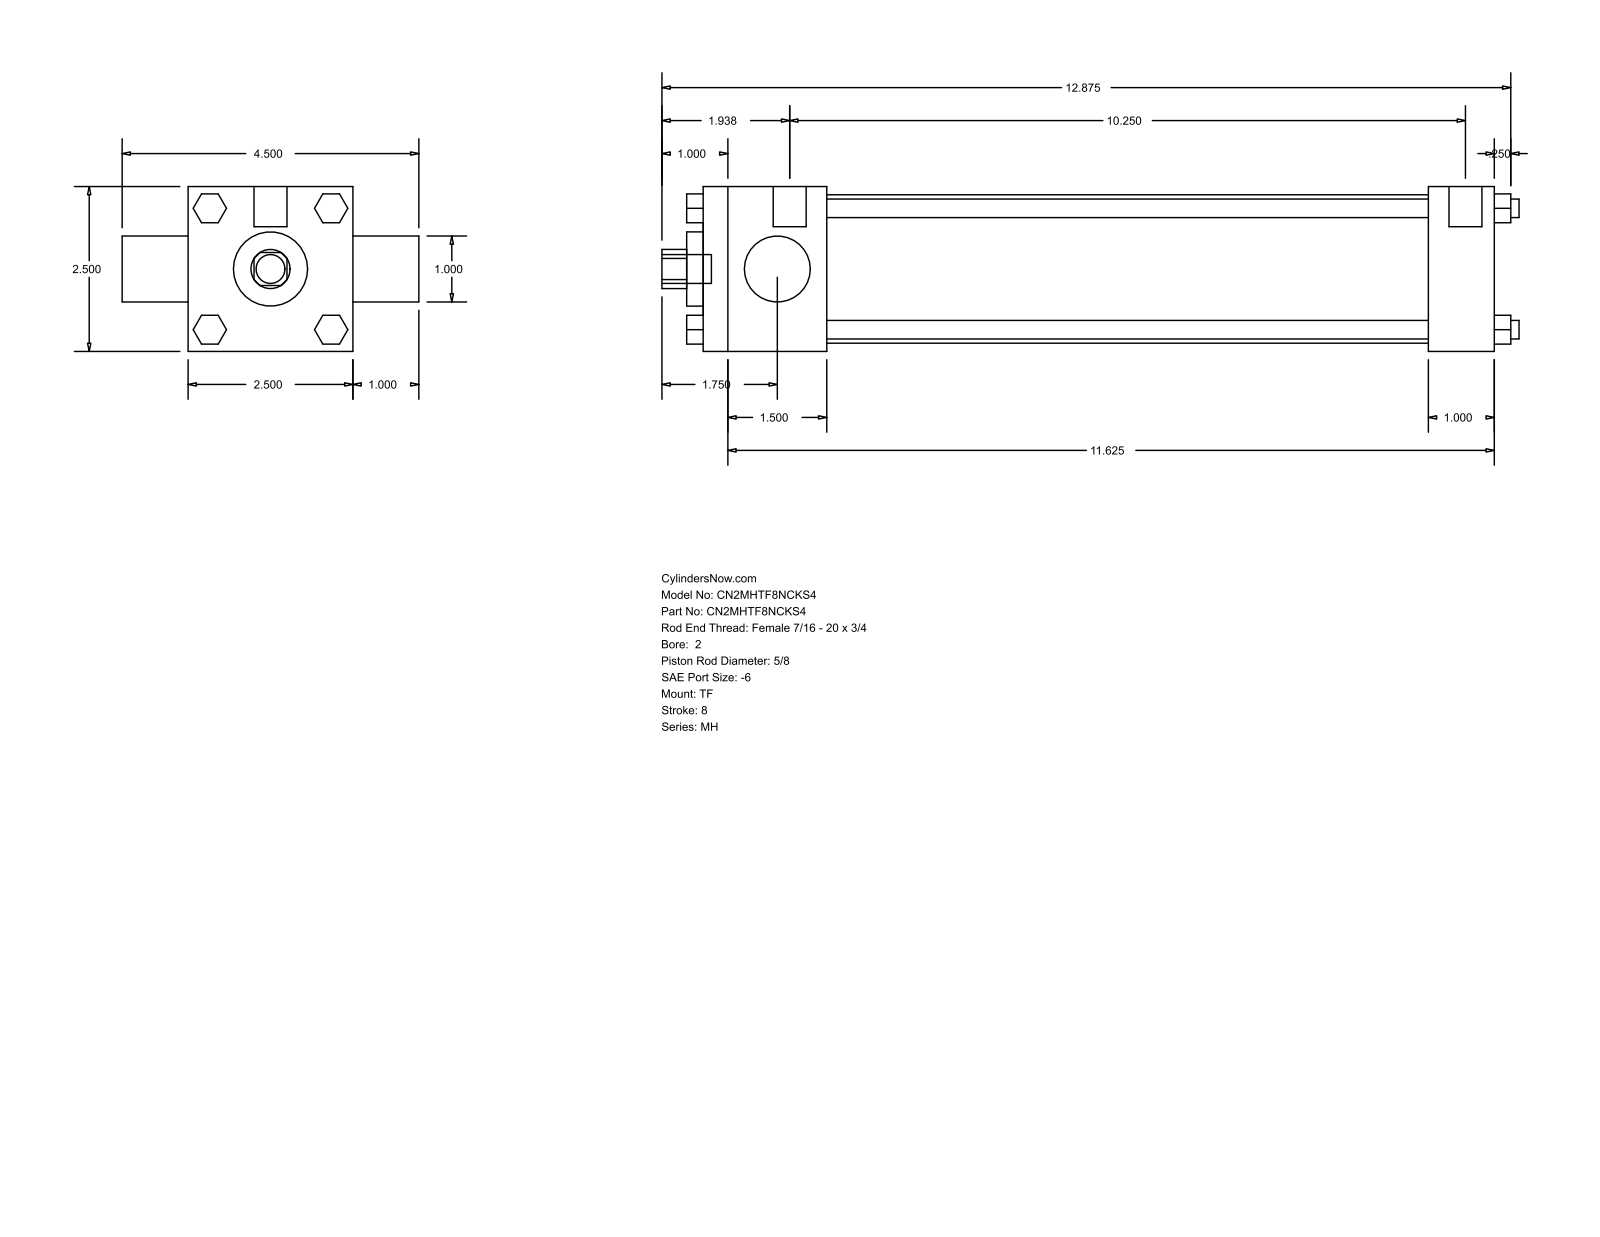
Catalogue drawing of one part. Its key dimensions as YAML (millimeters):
part_name: "MH_TF__0200_0.625"
step_written_by: "GSSL Pune (CONFIG_CONTROL_DESIGN)"
units: millimeters
bodies: {solids: 0, faces: 120, planar: 92, cylindrical: 28, other: 0}
overall_size: [330.2, 114.3, 63.5]
round_holes:
  - {diameter: 15.88, count: 1}
  - {diameter: 25.4, count: 1}
  - {diameter: 28.57, count: 1}
  - {diameter: 57.15, count: 1}
round_bosses_or_shafts:
  - {diameter: 7.14, count: 4}
  - {diameter: 5.56, count: 3}
  - {diameter: 12.7, count: 2}
  - {diameter: 11.11, count: 1}
partial_cylinders:
  - {radius: 7.54, count: 1}
face_to_face_distances: [63.5, 304.8, 47.62, 279.39, 231.77, 257.18, 25.41, 25.4, 88.9, 311.15]
